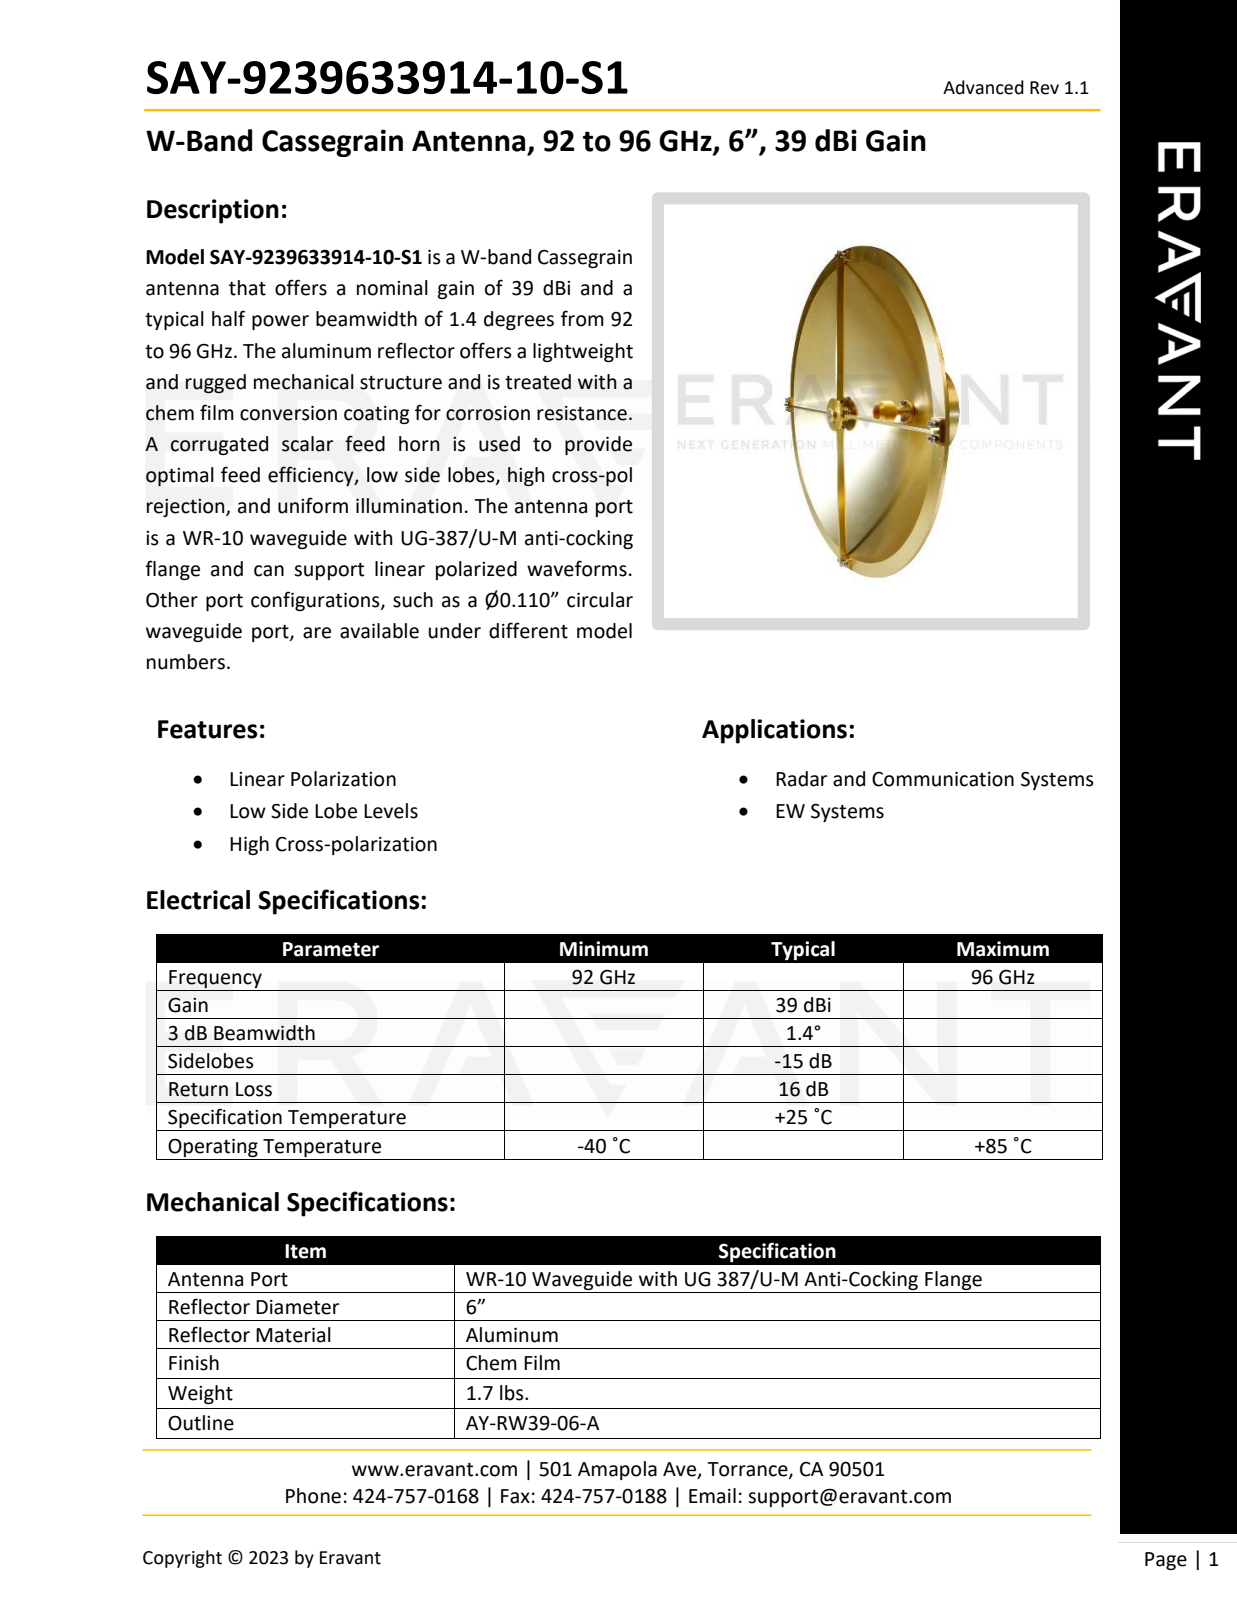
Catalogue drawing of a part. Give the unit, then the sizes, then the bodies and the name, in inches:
Units: inches
Overall size (bounding box): 6.85 × 6.85 × 3.49
Round holes (diameter × count): ⌀0.12 ×21, ⌀0.089 ×20, ⌀0.07 ×8, ⌀0.136 ×8, ⌀0.14 ×4, ⌀0.188 ×4, ⌀0.061 ×2, ⌀0.067 ×2, ⌀0.063 ×1, ⌀0.225 ×1, ⌀0.68 ×1, ⌀0.95 ×1
Round bosses / shafts (diameter × count): ⌀0.183 ×16, ⌀0.112 ×16, ⌀0.18 ×12, ⌀0.086 ×8, ⌀0.063 ×2, ⌀6.85 ×1, ⌀3.15 ×1, ⌀1.325 ×1
Partial cylindrical surfaces — rounded edges, fillets, slot ends (radius × count): R0.06 ×24, R0.01 ×8, R0.04 ×8, R0.18 ×1
Main face-to-face distances: 0.184, 2.629, 2.813, 0.079, 0.085, 0.073, 3.072, 0.444, 0.26, 2.922
Hole centre spacings: 3.476, 3.75, 2.641, 4.519, 4.519, 6.382, 0.215, 0.281
Volume: 16.14 in³ · Surface area: 128.9 in²
Bodies: 45 solids, 1157 faces (436 planar, 321 cylindrical, 400 other)
Part name (STEP PRODUCT): SAY-9239633914-10-S1
STEP written by: SolidWorks 2021 (CONFIG_CONTROL_DESIGN)
